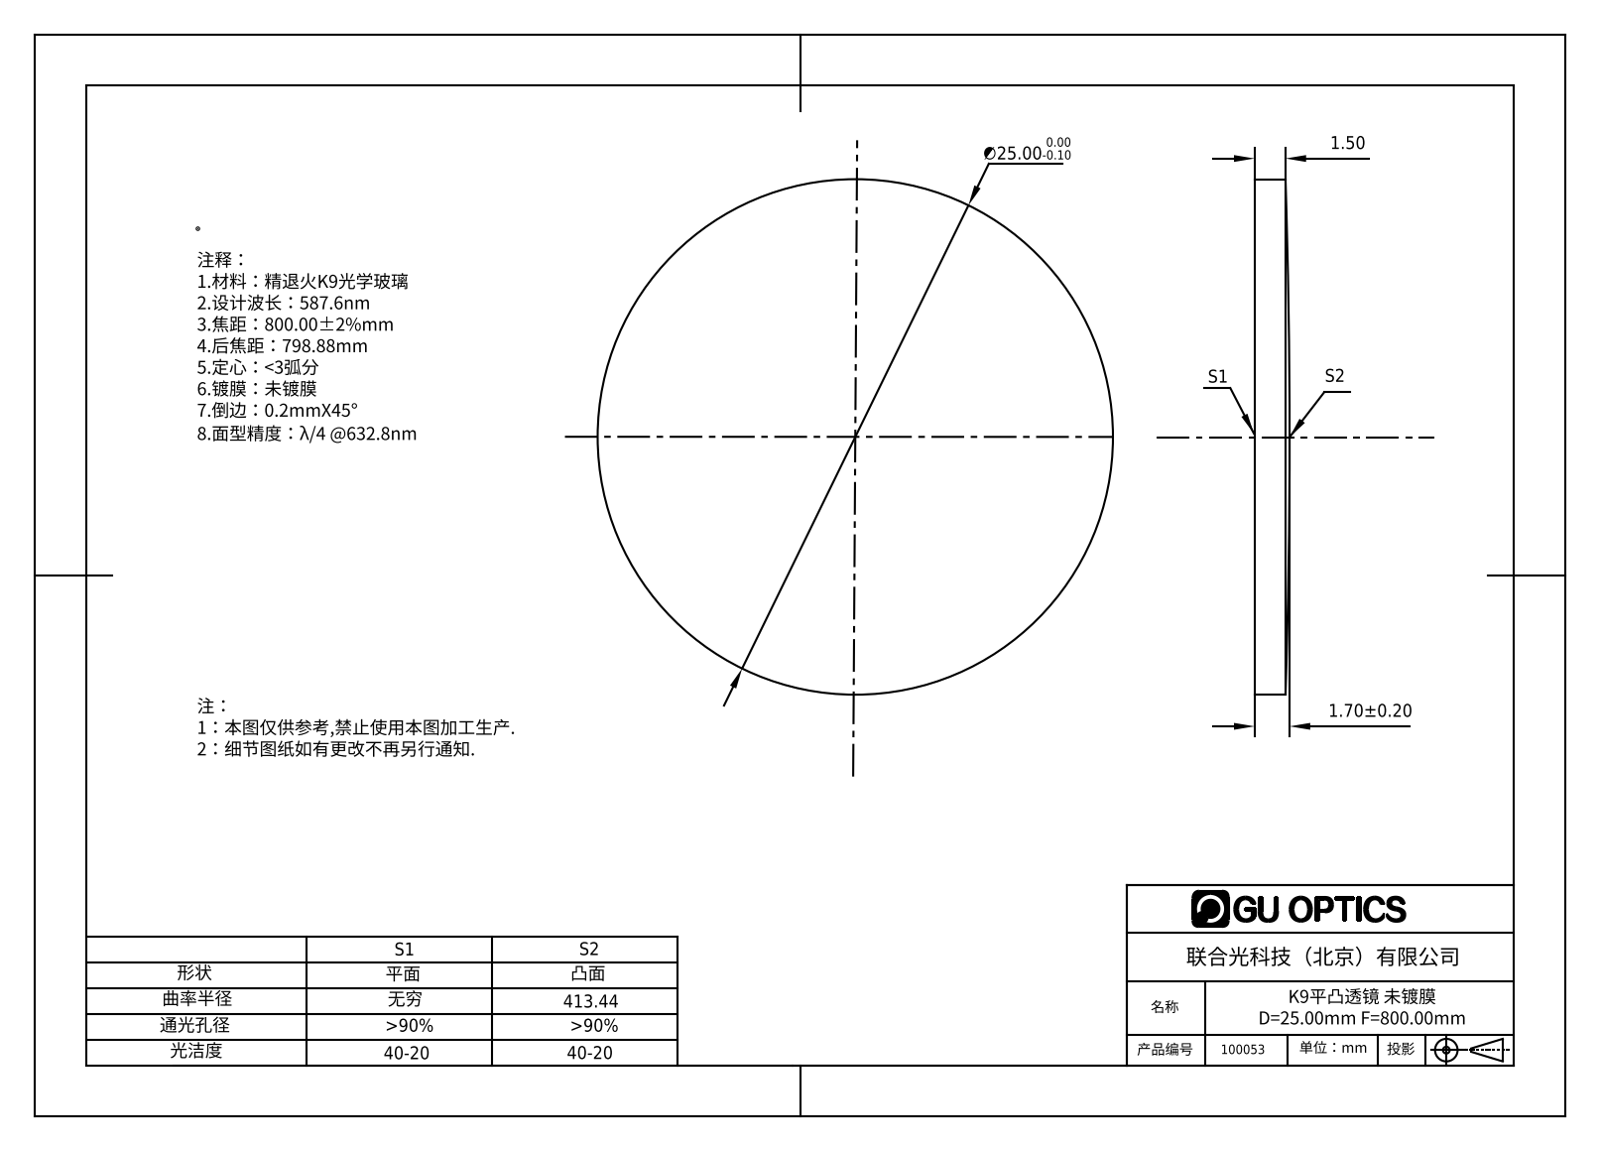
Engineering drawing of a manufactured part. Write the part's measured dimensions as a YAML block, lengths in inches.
part_name: "100053"
step_written_by: "SolidWorks 2016 (AUTOMOTIVE_DESIGN)"
units: inches
bodies: {solids: 1, faces: 5, planar: 1, cylindrical: 2, other: 2}
overall_size: [0.984, 0.984, 0.067]
volume: 0.048
surface_area: 1.705
round_bosses_or_shafts:
  - {diameter: 0.984, count: 1}
